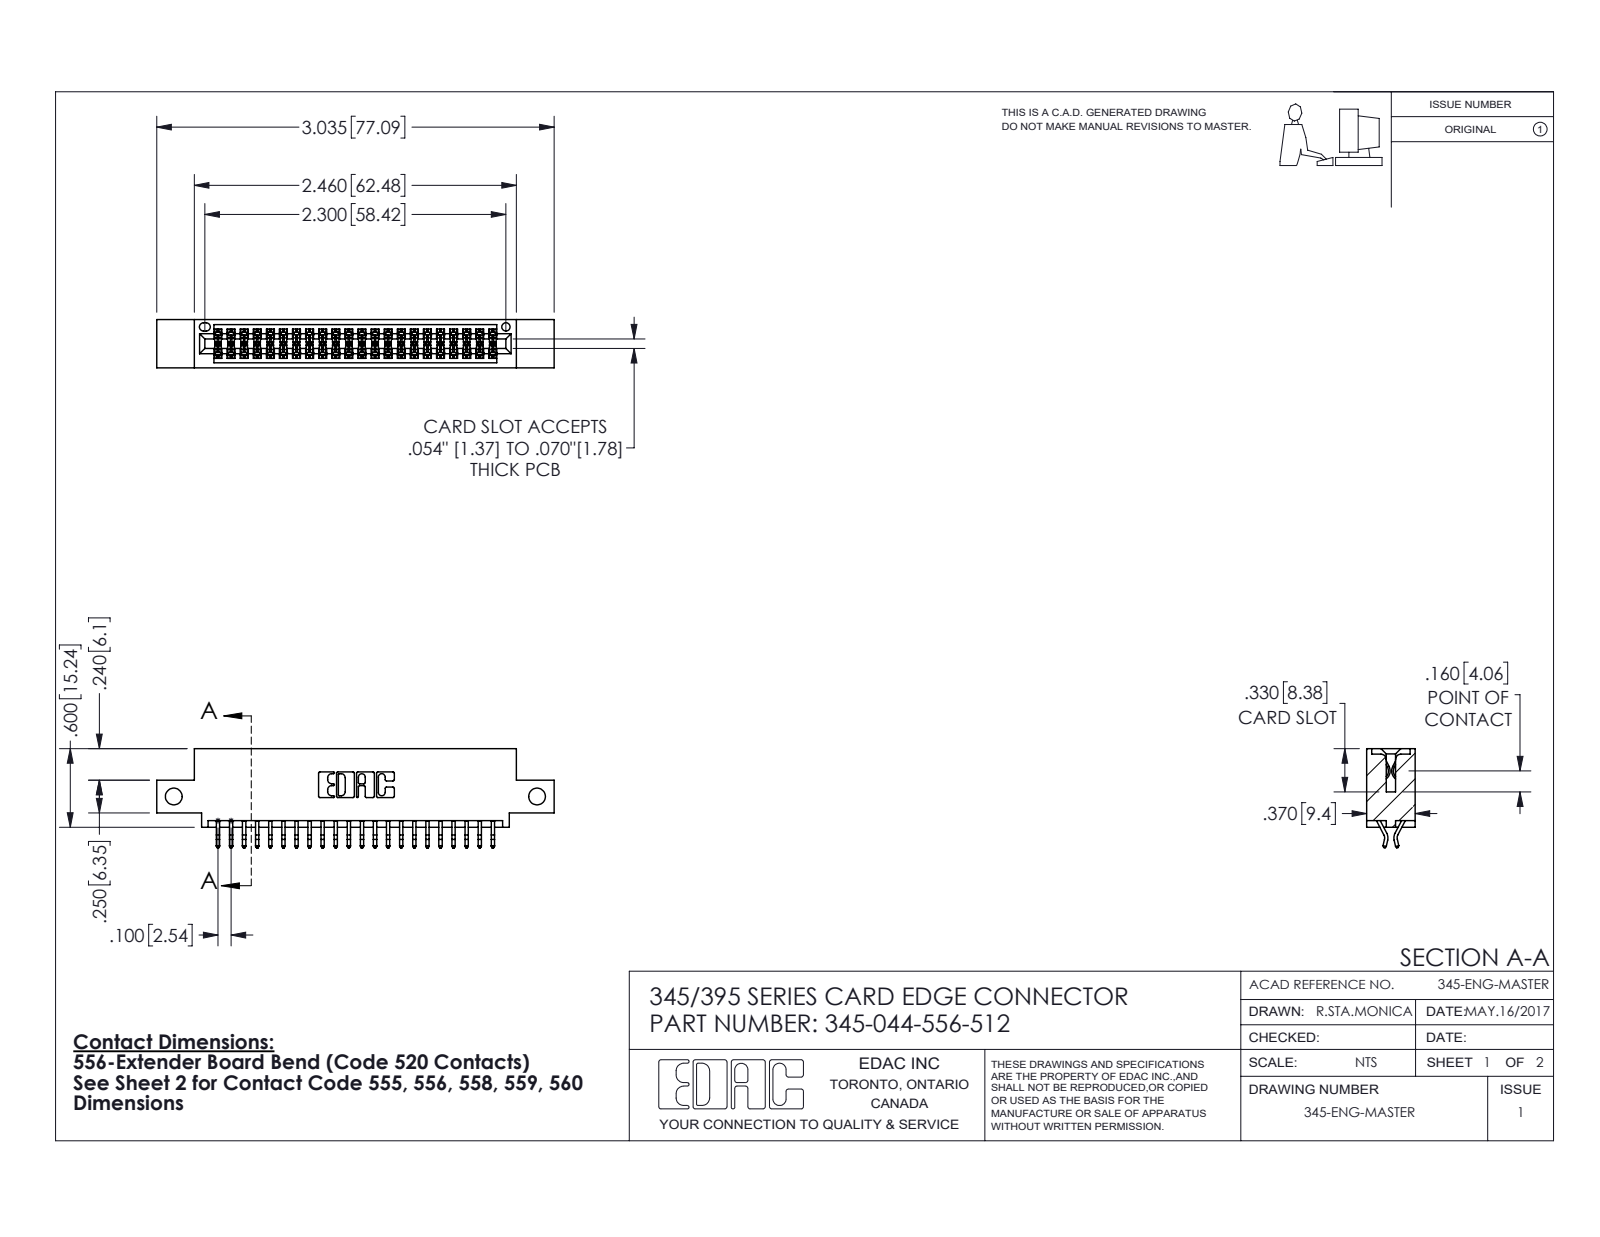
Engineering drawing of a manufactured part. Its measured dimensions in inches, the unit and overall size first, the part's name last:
Units: inches
Overall size (bounding box): 3.035 × 0.757 × 0.37
Round holes (diameter × count): ⌀0.128 ×2, ⌀0.064 ×1
Partial cylindrical surfaces — rounded edges, fillets, slot ends (radius × count): R0.006 ×66, R0.01 ×22, R0.007 ×6, R0.031 ×6, R0.026 ×3, R0.01 ×2, R0.014 ×2, R0.019 ×2
Main face-to-face distances: 0.298, 0.072, 0.37, 0.2, 0.025, 0.098, 0.272, 0.225, 0.175, 0.149
Hole centre spacings: 2.775
Volume: 0.436 in³ · Surface area: 15.63 in²
Bodies: 45 solids, 2594 faces (1712 planar, 882 cylindrical, 0 other)
Part name (STEP PRODUCT): 345-044-556-512; 345-292-001_556 Tail; 345 Part_0.110 Offset - Side Mount
STEP written by: SolidWorks 2016 (CONFIG_CONTROL_DESIGN)
